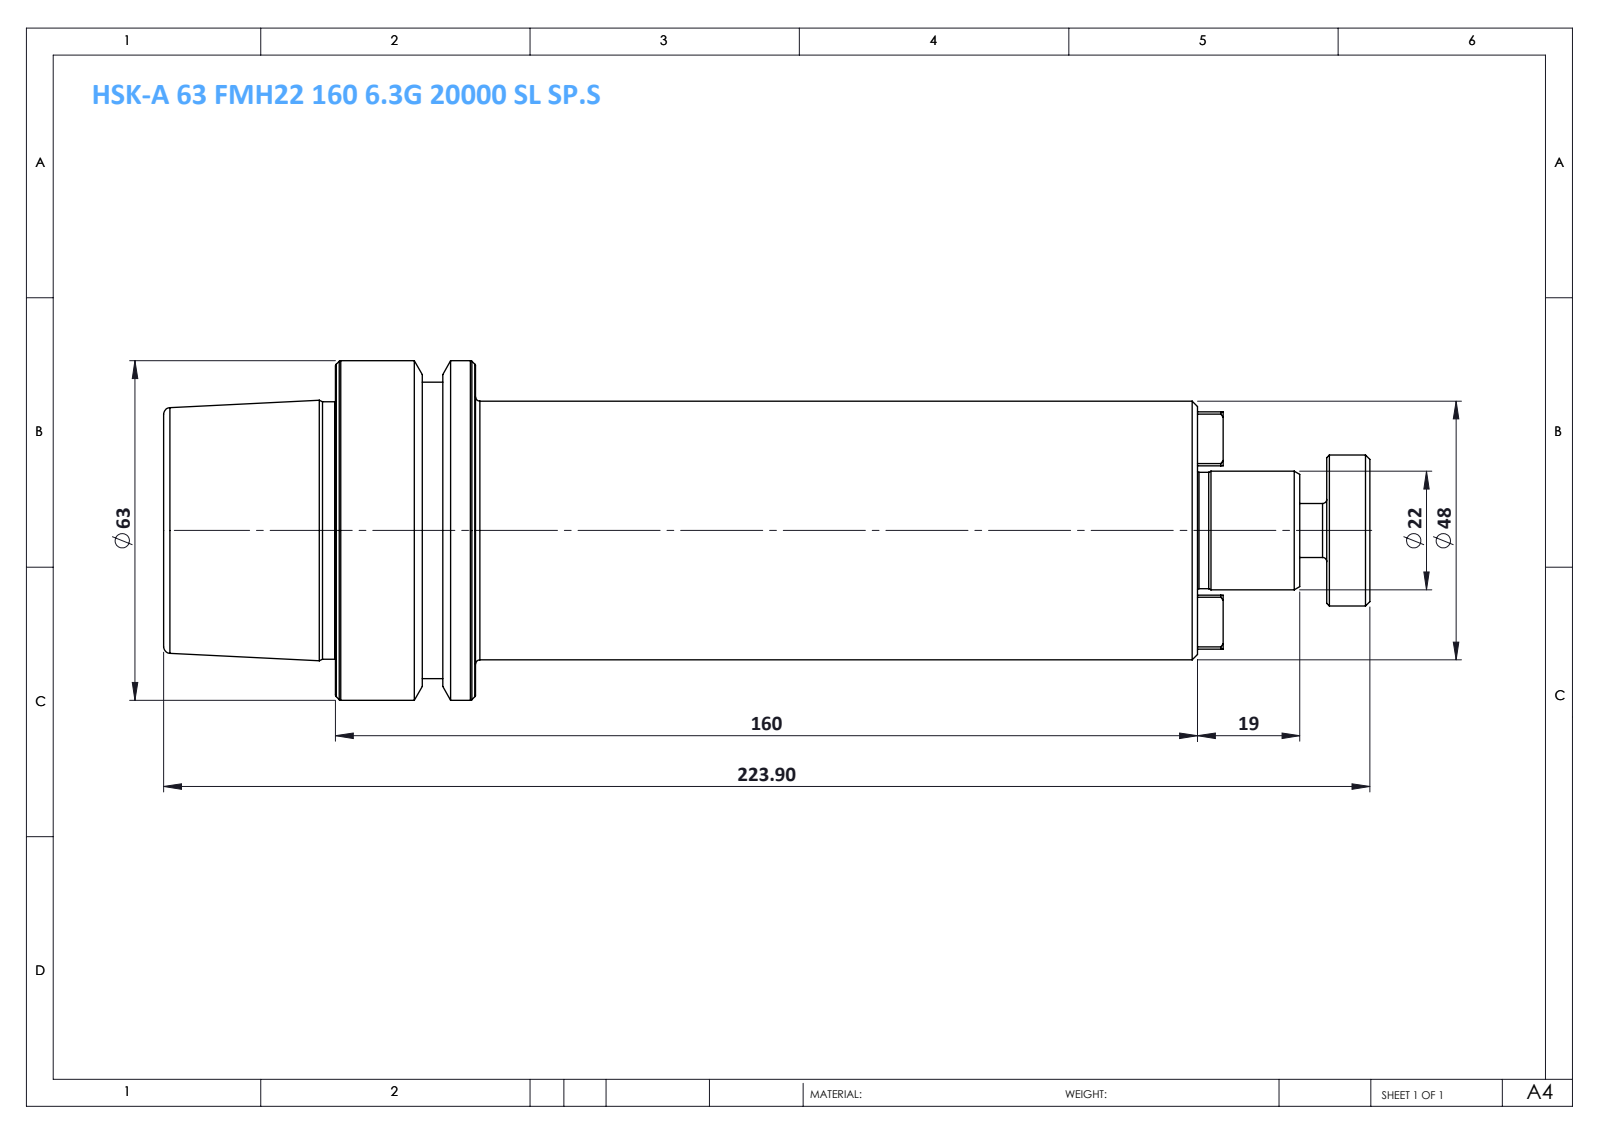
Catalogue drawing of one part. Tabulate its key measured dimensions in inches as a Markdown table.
| quantity | value |
| --- | --- |
| part name | HSK-A 63 FMH22 160 6.3G 20000 SL SP.S |
| STEP written by | SolidWorks 2014 (CONFIG_CONTROL_DESIGN) |
| units | inches |
| bodies | 1 solid, 99 faces (37 planar, 18 cylindrical, 44 other) |
| overall size | 8.815 × 2.48 × 2.48 |
| volume | 23.7 in³ |
| surface area | 62.38 in² |
| round bosses / shafts (diameter × count) | 2.48 × 1, 2.165 × 1, 1.89 × 1, 1.881 × 1, 1.102 × 1, 0.866 × 1, 0.85 × 1, 0.394 × 1 |
| main face-to-face distances | 2.28, 5.276, 7.555, 6.299, 1.024, 1.256, 1.26, 6.535, 7.559, 8.815 |
